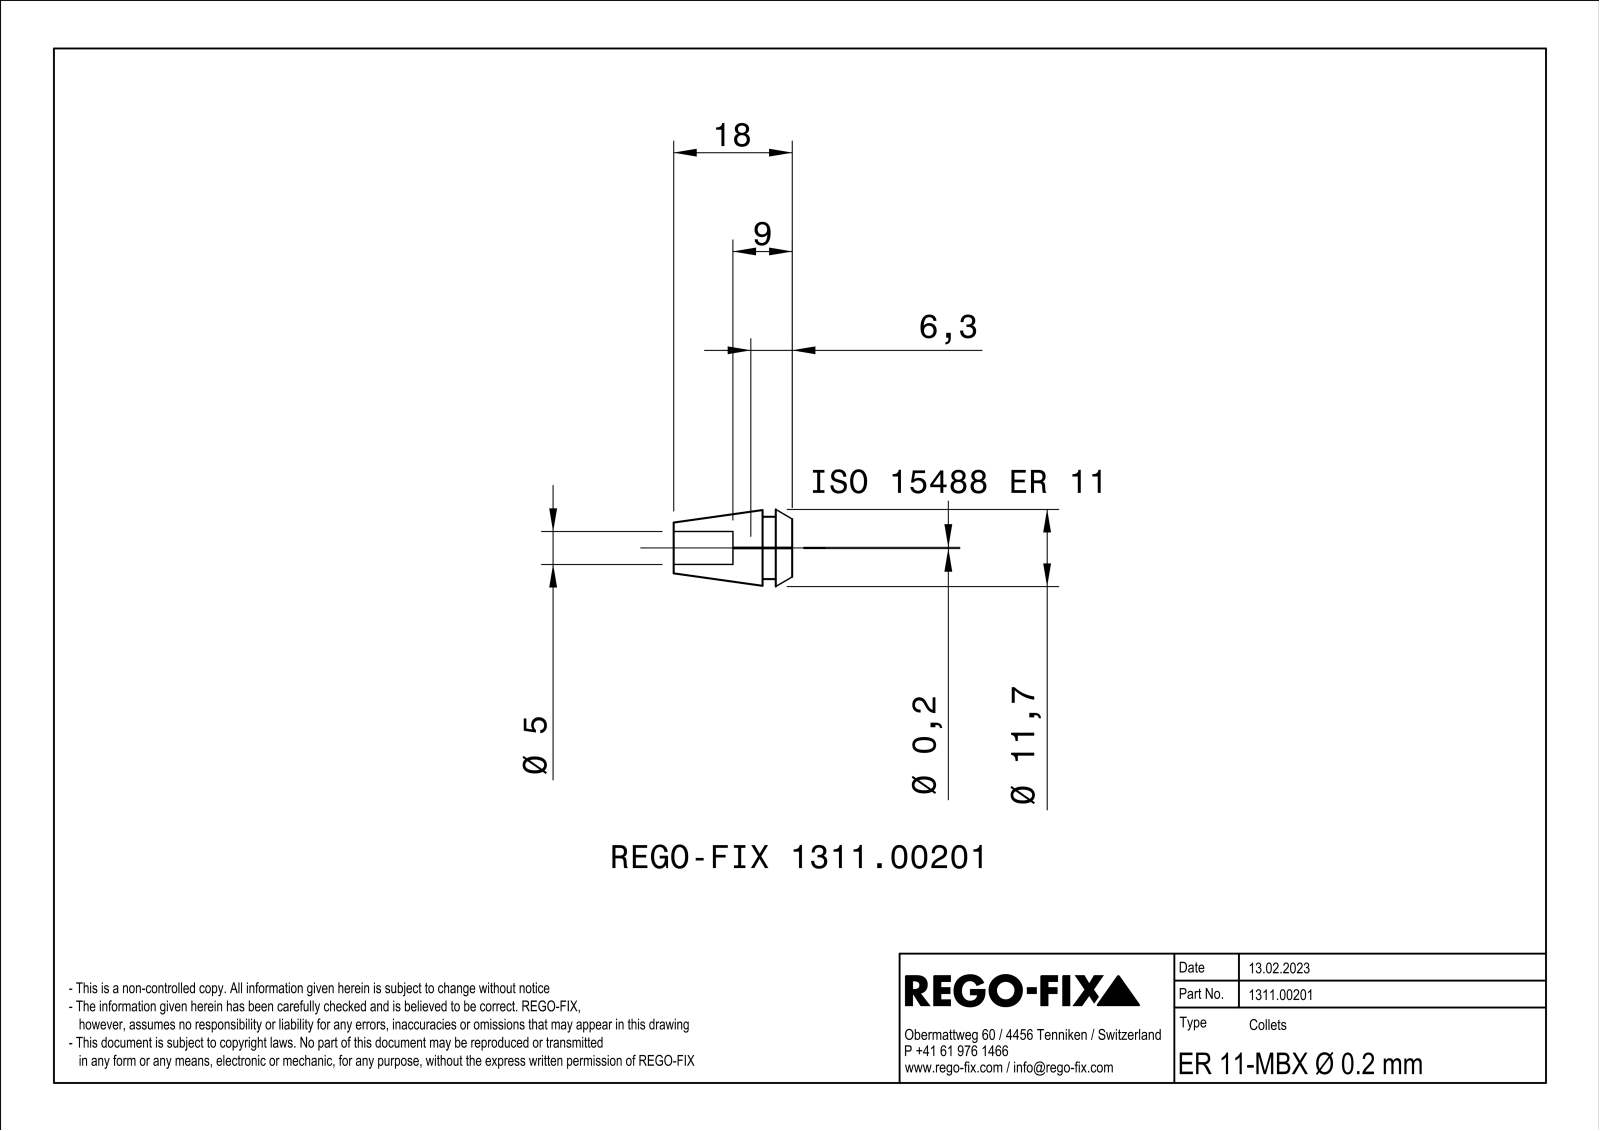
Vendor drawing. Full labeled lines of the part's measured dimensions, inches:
Part name (STEP PRODUCT): NOCUT
STEP written by: SIEMENS PLM Software Solid Edge ST10 (AUTOMOTIVE_DESIGN)
Units: inches
Bodies: 1 solid, 91 faces (26 planar, 19 cylindrical, 46 other)
Overall size (bounding box): 0.709 × 0.449 × 0.448
Volume: 0.061 in³ · Surface area: 1.955 in²
Round holes (diameter × count): ⌀0.059 ×3, ⌀0.197 ×1
Round bosses / shafts (diameter × count): ⌀0.374 ×1
Partial cylindrical surfaces — rounded edges, fillets, slot ends (radius × count): R0.984 ×3, R0.004 ×1
Main face-to-face distances: 0.031, 0.013, 0.018, 0.177, 0.354, 0.709, 0.531, 0.098, 0.079, 0.61
Hole centre spacings: 0.067, 0.116
